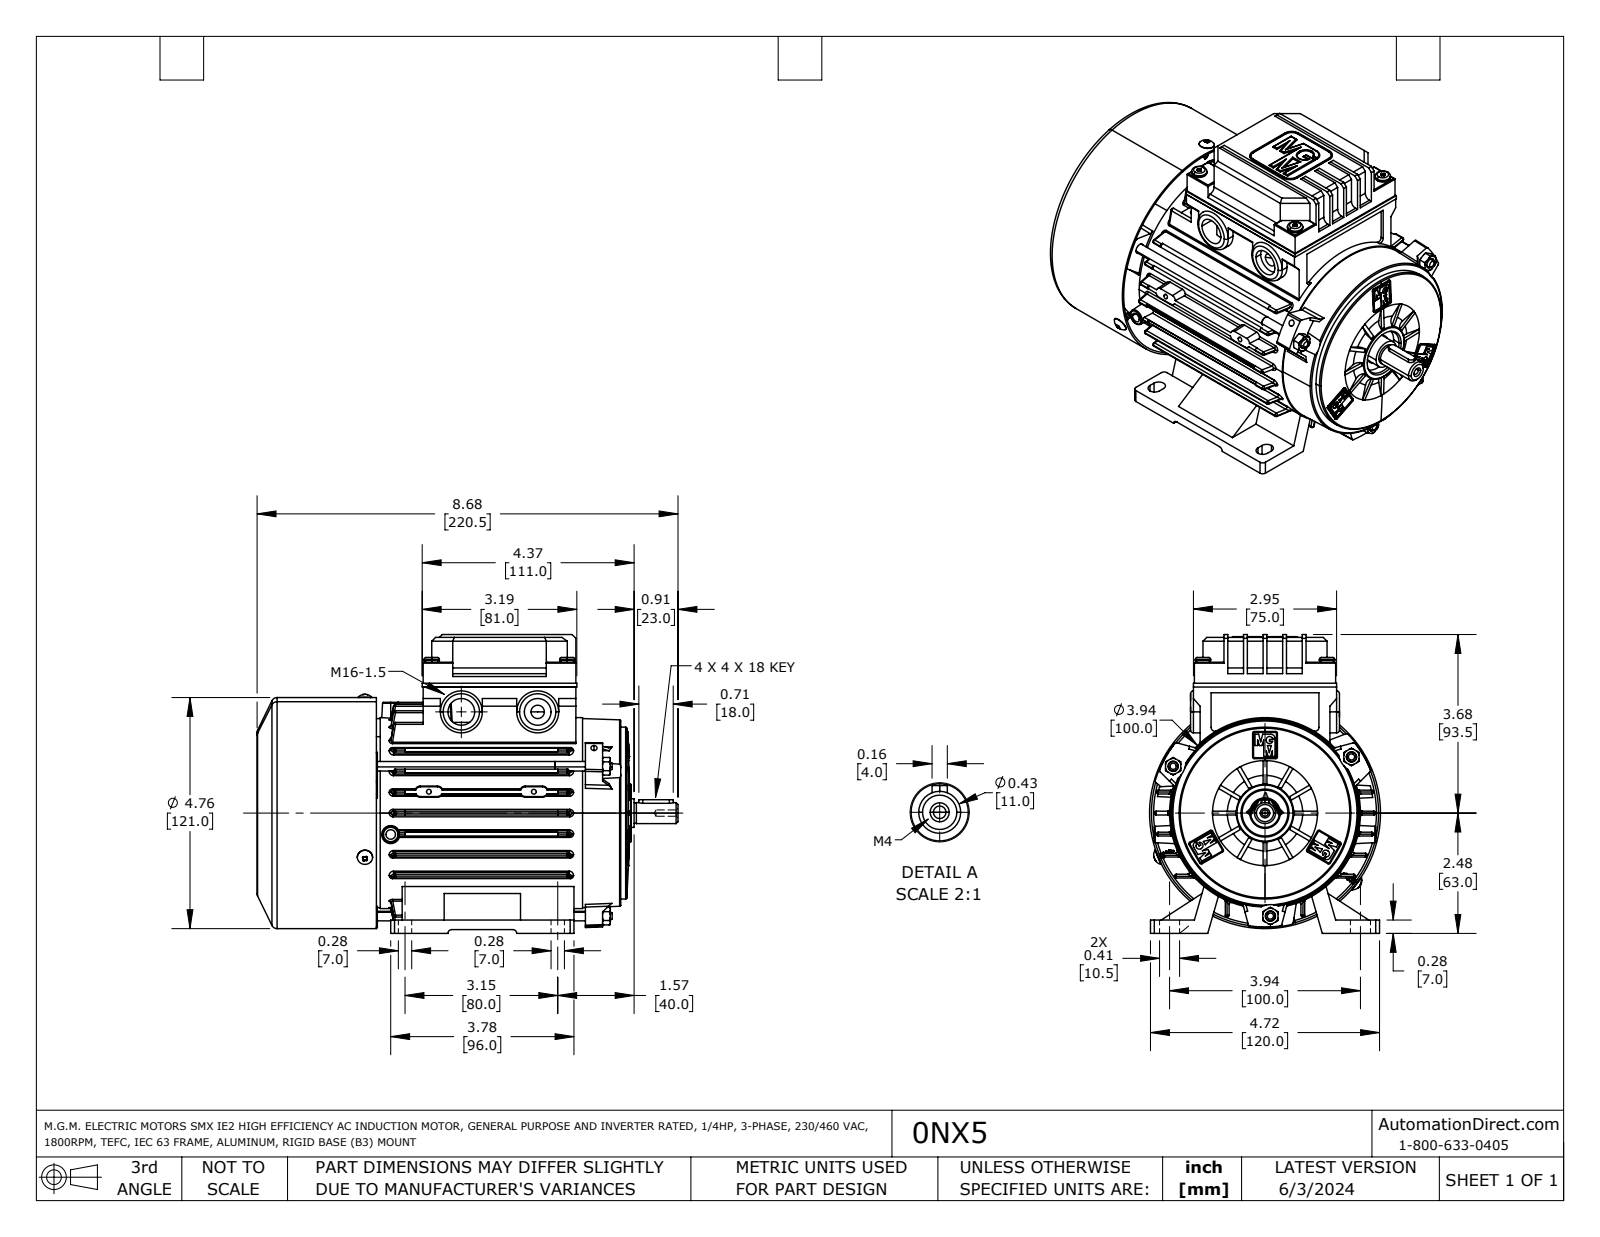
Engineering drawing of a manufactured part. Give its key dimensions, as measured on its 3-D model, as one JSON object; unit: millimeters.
{"part_name": "0NX5", "step_written_by": "SolidWorks 2021 (AUTOMOTIVE_DESIGN)", "units": "millimeters", "bodies": {"solids": 24, "faces": 3325, "planar": 1275, "cylindrical": 1061, "other": 989}, "overall_size": [220.5, 156.5, 121], "volume_mm3": 482100, "surface_area_mm2": 324100, "round_holes": [[3, 12], [3.3, 8], [4, 7], [5.5, 7], [3.2, 6], [7, 3], [2.5, 2], [5, 2], [14, 2], [8, 1], [16, 1], [24, 1]], "round_bosses_or_shafts": [[3, 10], [8, 7], [3.5, 4], [5, 3], [2, 3], [121, 1], [100, 1], [95, 1]], "partial_cylinders_radius": [[1, 275], [0.4, 36], [0.5, 36], [0.2, 32], [2, 32], [0.4, 24], [0.9, 24], [0.1, 16]], "face_to_face_distances": [2, 22, 24, 11, 33, 124, 44, 13, 20, 55], "hole_center_spacings": [12.1, 14.5, 19, 28, 31, 31, 39.6, 40]}
